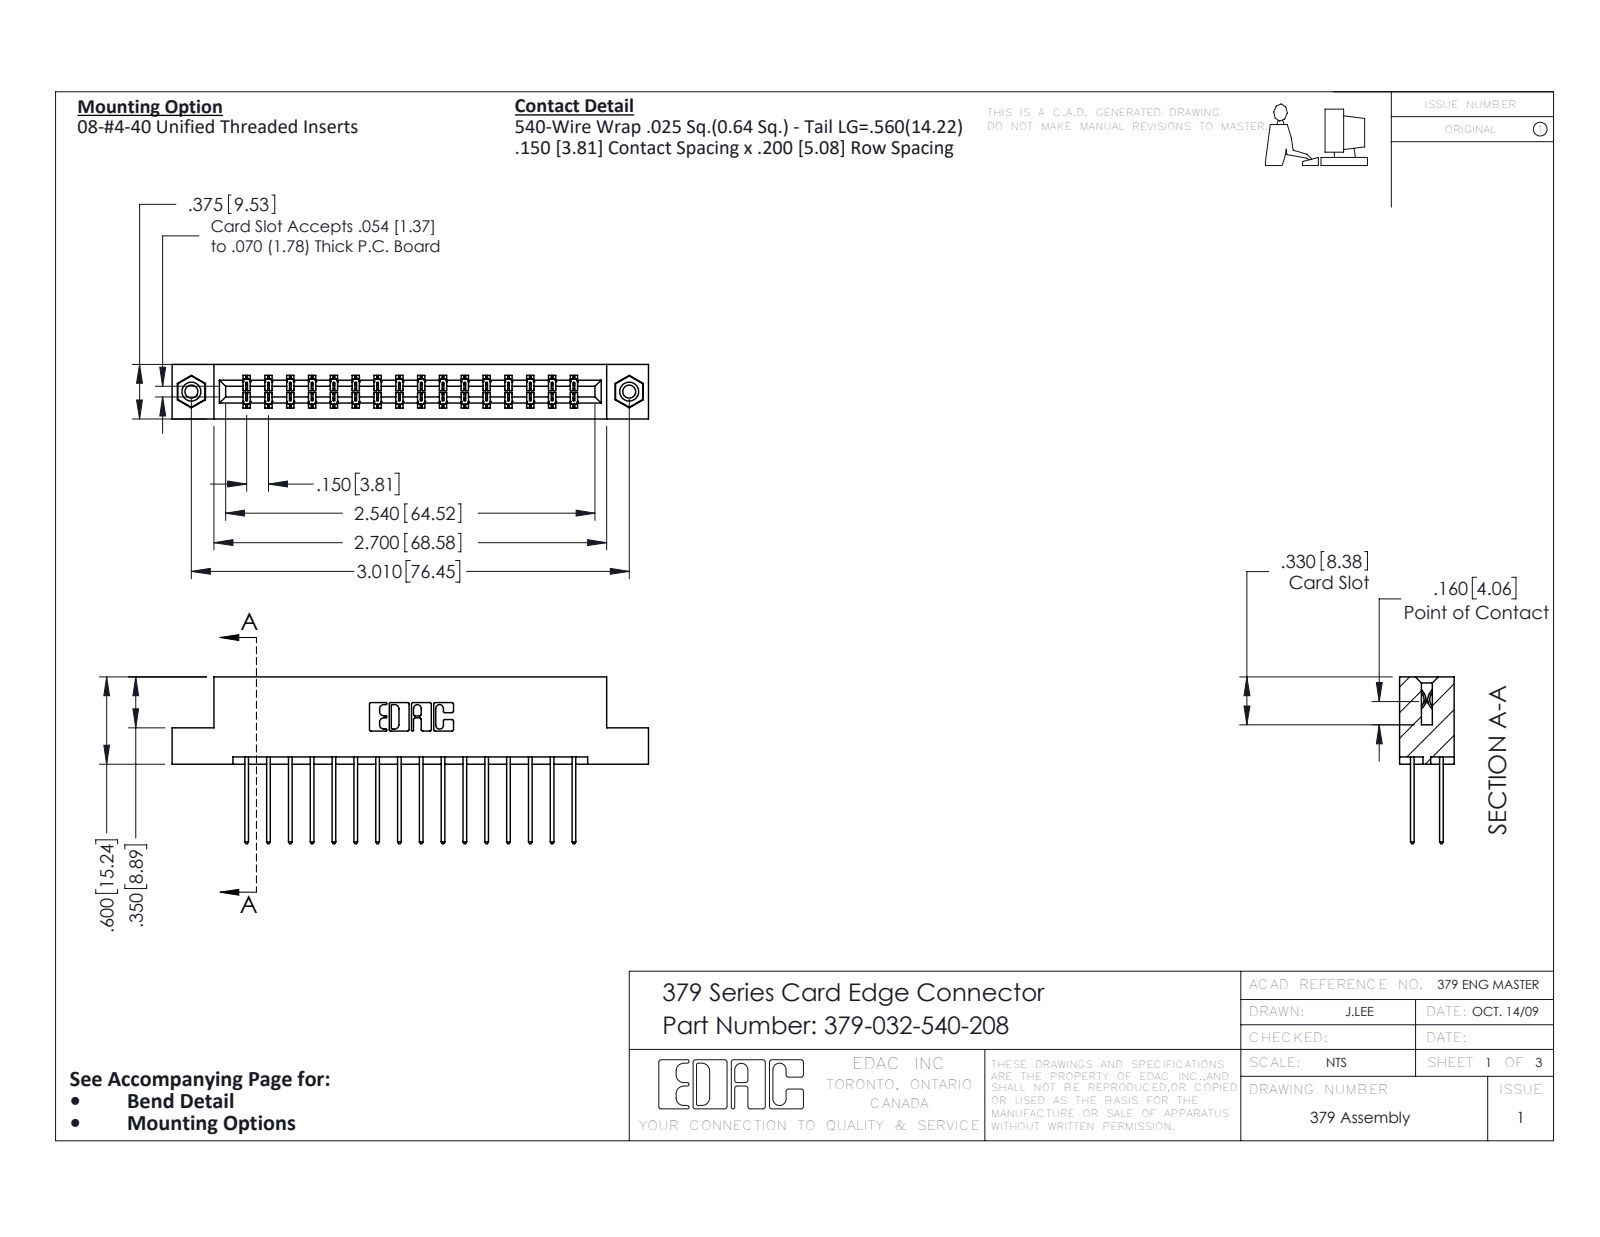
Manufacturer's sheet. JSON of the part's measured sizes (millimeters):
{"part_name": "345-292-001_345-293-140; 379-032-540-208; 379 Part_Flush - .156 Dia - TI; 345-250-001_345-250-003-102", "step_written_by": "SolidWorks 2020 (CONFIG_CONTROL_DESIGN)", "units": "millimeters", "bodies": {"solids": 35, "faces": 1838, "planar": 1254, "cylindrical": 568, "other": 16}, "overall_size": [83.2, 29.1, 9.5], "volume_mm3": 8650, "surface_area_mm2": 10100, "round_holes": [[2.3, 2], [3.2, 2], [4, 2]], "round_bosses_or_shafts": [[3.9, 2]], "partial_cylinders_radius": [[0.2, 63], [0.3, 32], [0.3, 22], [0.2, 6], [0.8, 6], [0.7, 3], [0.4, 2], [0.6, 2]], "face_to_face_distances": [7.6, 1.9, 5.1, 2.5, 9.5, 7, 3.8, 1.3, 15.2, 0.6], "hole_center_spacings": [76.5]}
